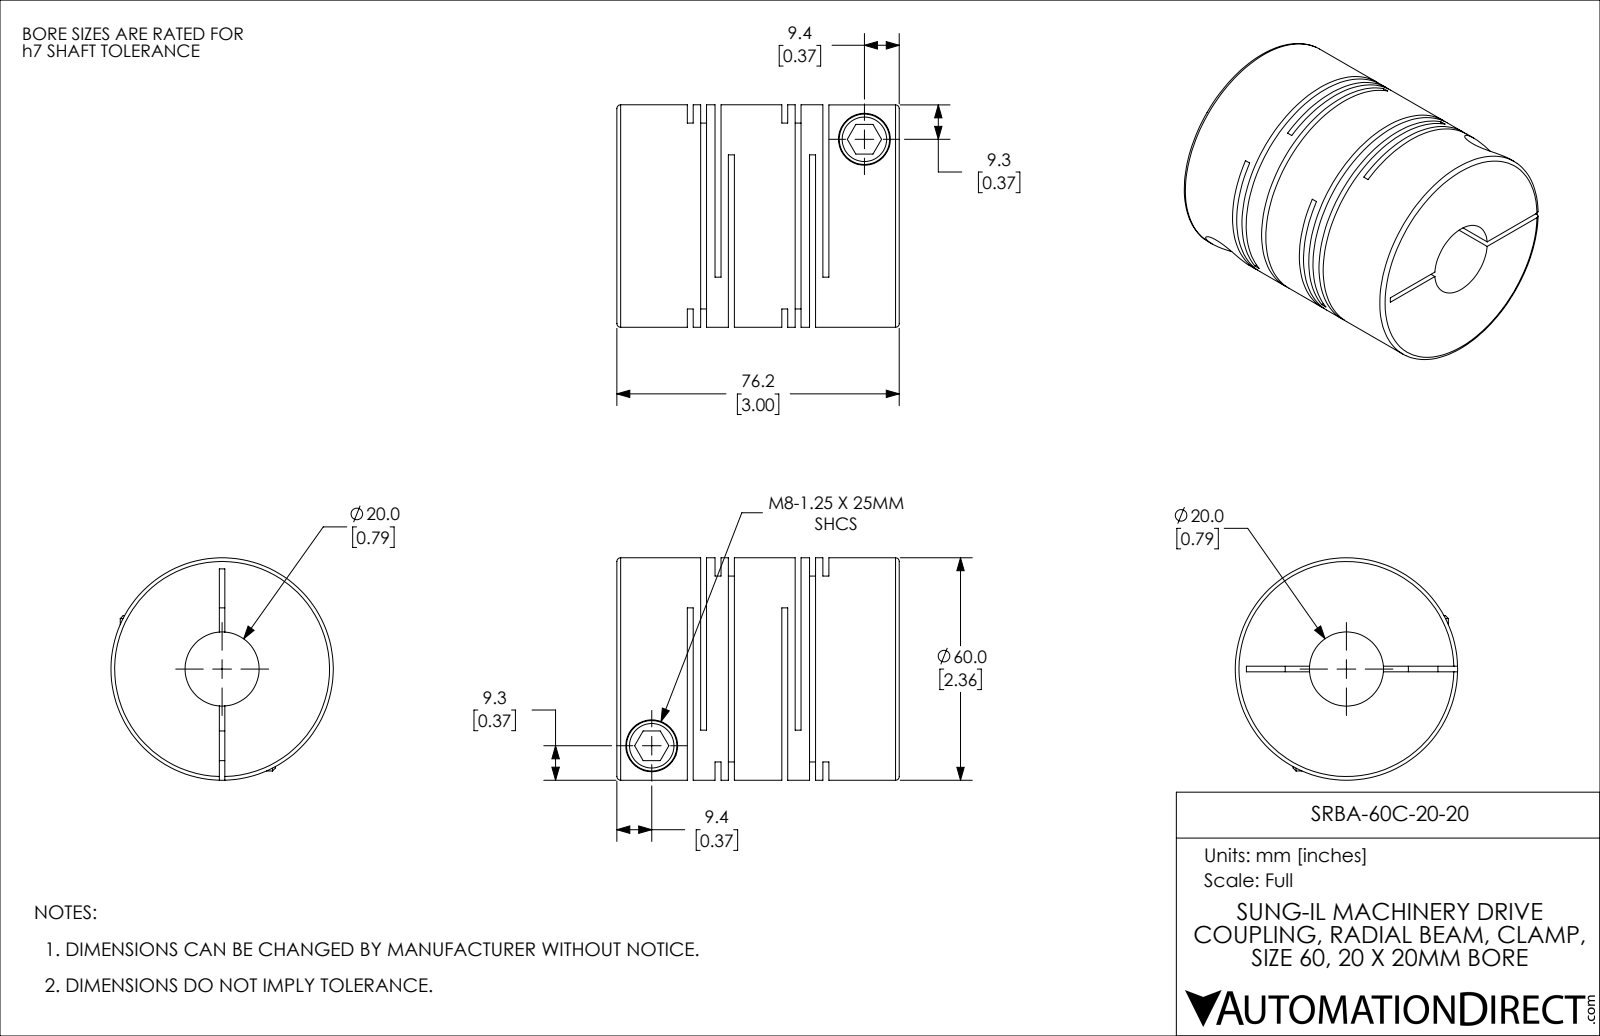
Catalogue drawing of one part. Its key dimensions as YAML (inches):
part_name: "SRBA-60C-20-20"
step_written_by: "SolidWorks 2021 (CONFIG_CONTROL_DESIGN)"
units: inches
bodies: {solids: 1, faces: 115, planar: 60, cylindrical: 42, other: 13}
overall_size: [3, 2.362, 2.362]
volume: 9.781
surface_area: 91.64
round_holes:
  - {diameter: 0.315, count: 2}
  - {diameter: 0.551, count: 2}
  - {diameter: 0.787, count: 1}
round_bosses_or_shafts:
  - {diameter: 0.535, count: 2}
  - {diameter: 2.362, count: 1}
face_to_face_distances: [0.063, 0.142, 0.295, 1.004, 1.299, 0.232, 0.941, 0.709, 0.079, 0.154]
